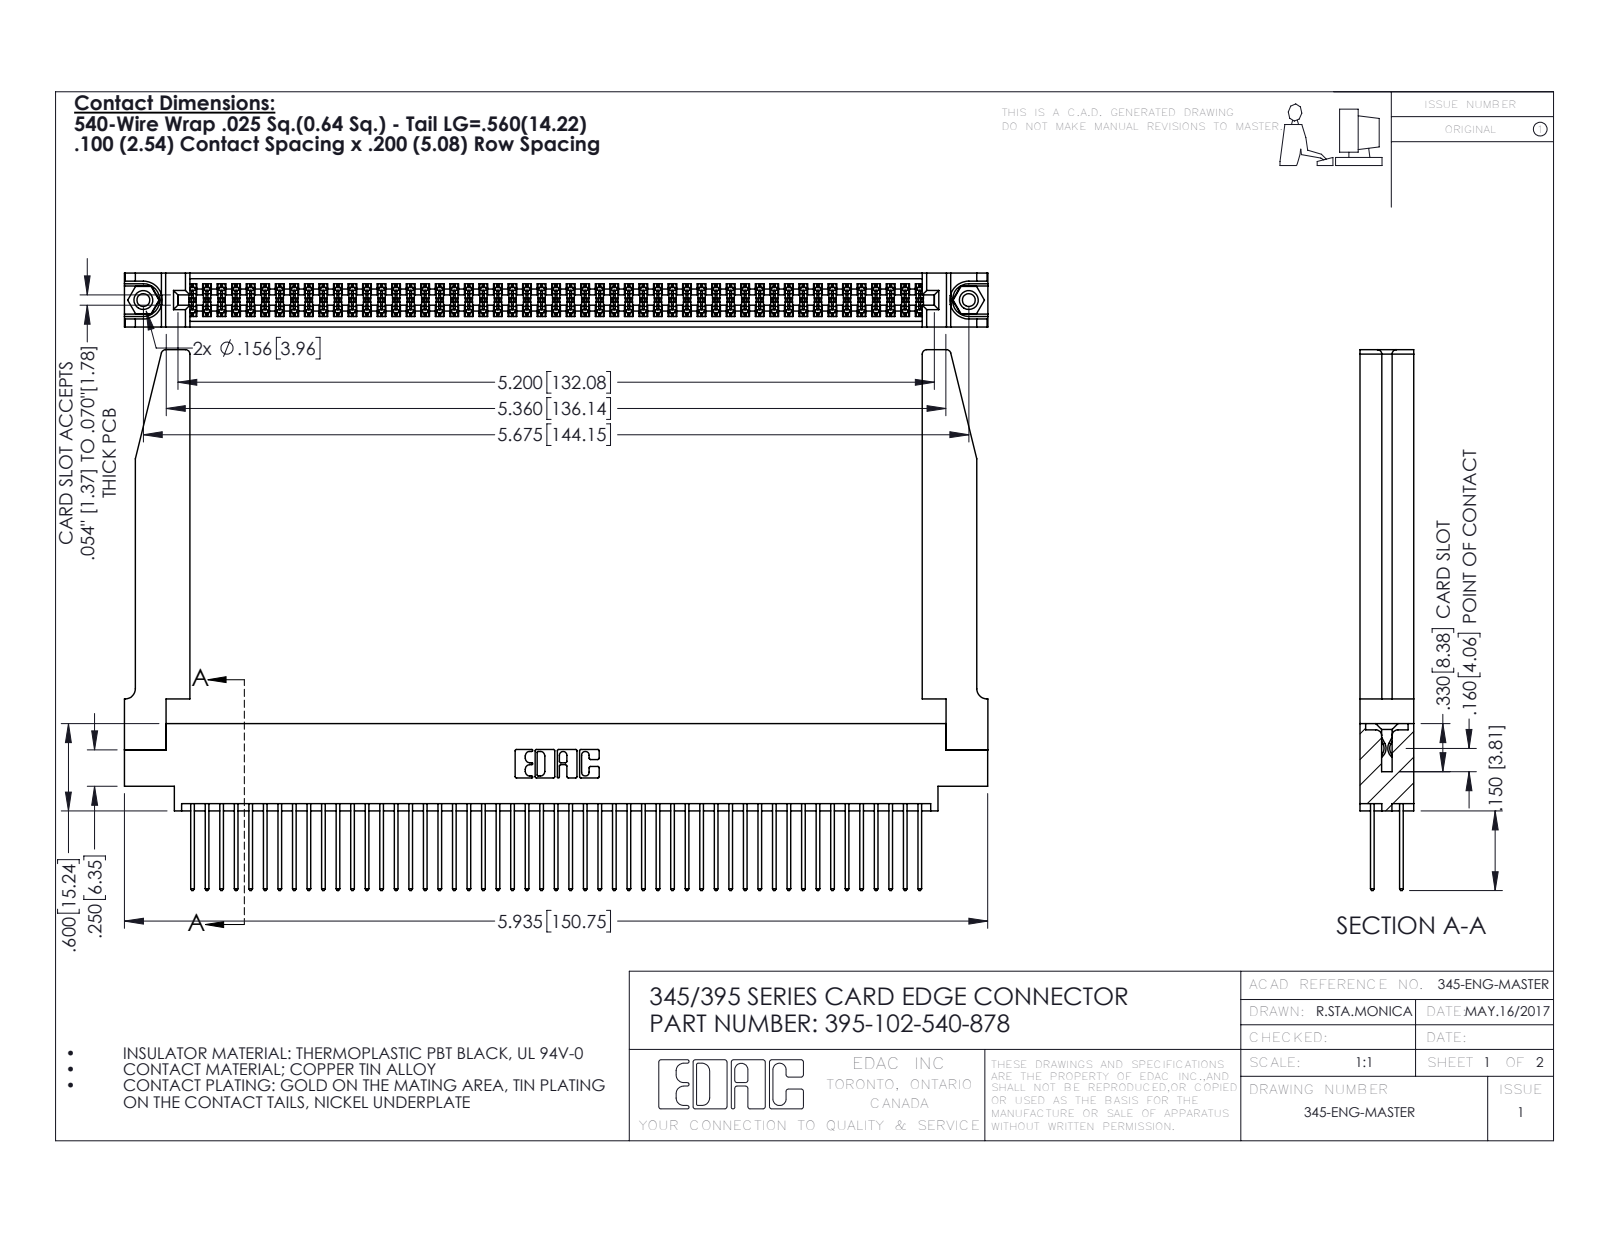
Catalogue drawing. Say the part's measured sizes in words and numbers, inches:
The part is named "345-220-078_345-220-078; 345 Part_0.170 Offset - 0.156 Dia-TH; 345-250-001_345-250-001-102; 345-292-001_345-293-140 (+1 more)". Its 3-D file was written by "SolidWorks 2016 (CONFIG_CONTROL_DESIGN)". It is 107 solids with 5464 faces: 3592 planar, 1820 cylindrical and 52 other. Overall it measures 5.936 by 3.717 by 0.37 inches. Its volume is 1.39 cubic inches and its surface area 48.25 square inches. Round holes: 2 of diameter 0.089, 2 of diameter 0.125, 2 of diameter 0.156, 1 of diameter 0.064. Round bosses or shafts: 2 of diameter 0.155. Partial cylindrical surfaces (rounded edges, fillets, slot ends): 153 of radius 0.006, 102 of radius 0.01, 22 of radius 0.01, 8 of radius 0.03, 6 of radius 0.007, 6 of radius 0.031, 3 of radius 0.026, 2 of radius 0.014. The main face-to-face distances are 0.072, 0.298, 0.37, 0.098, 0.272, 0.025, 0.2, 0.225, 0.175, 0.148. The hole center spacings are 0.27, 5.439, 5.675.
